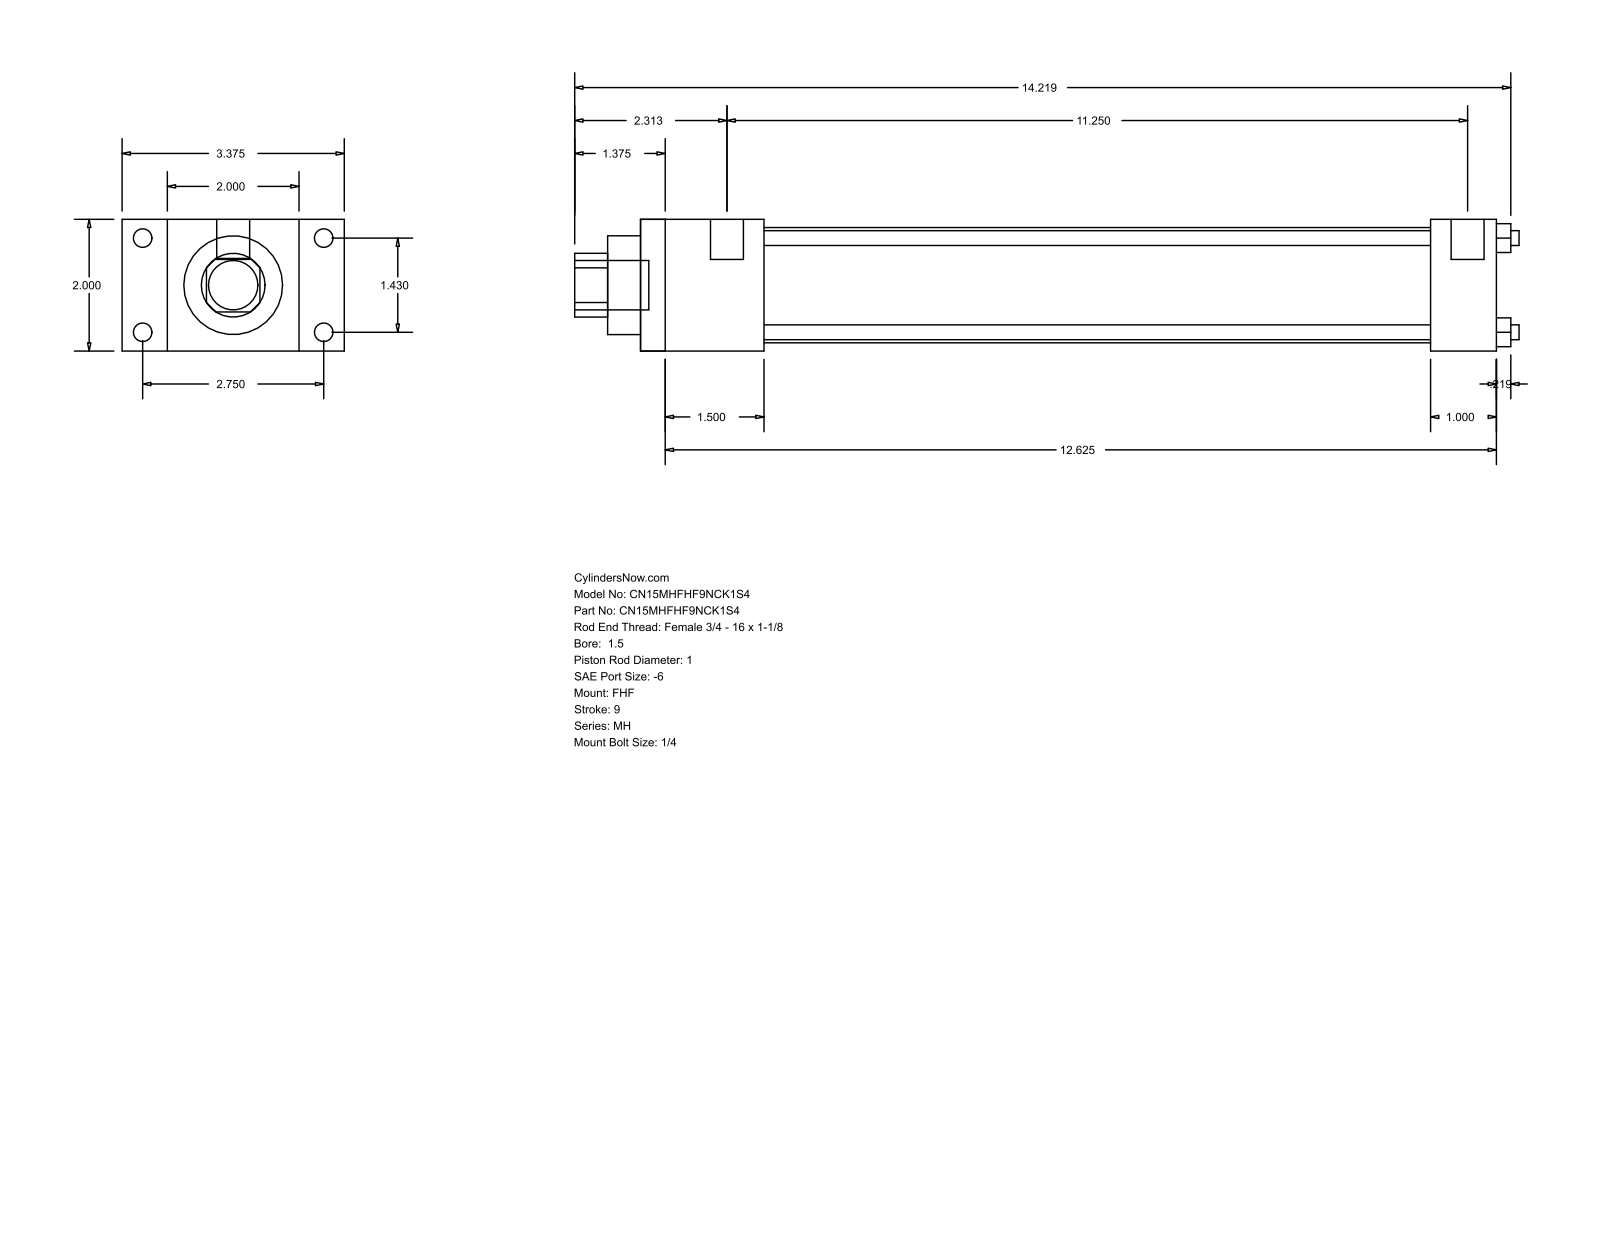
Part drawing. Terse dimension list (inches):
name: MH_FHF__0150_1
written by: GSSL Pune (CONFIG_CONTROL_DESIGN)
unit: in
bodies: 0 solids, 88 faces (60 planar, 28 cylindrical, 0 other)
size: 14.344 × 3.375 × 2
holes: 4× ⌀0.225, 1× ⌀1, 1× ⌀1.5, 1× ⌀1.75
bosses: 4× ⌀0.281, 4× ⌀0.219, 2× ⌀0.5, 1× ⌀0.75
rounds: 1× R0.484
face distances: 2, 0.687, 2.687, 1.875, 3.375, 13, 11.125, 1, 12, 10.125
hole spacings: 1.011, 1.43, 2.022
